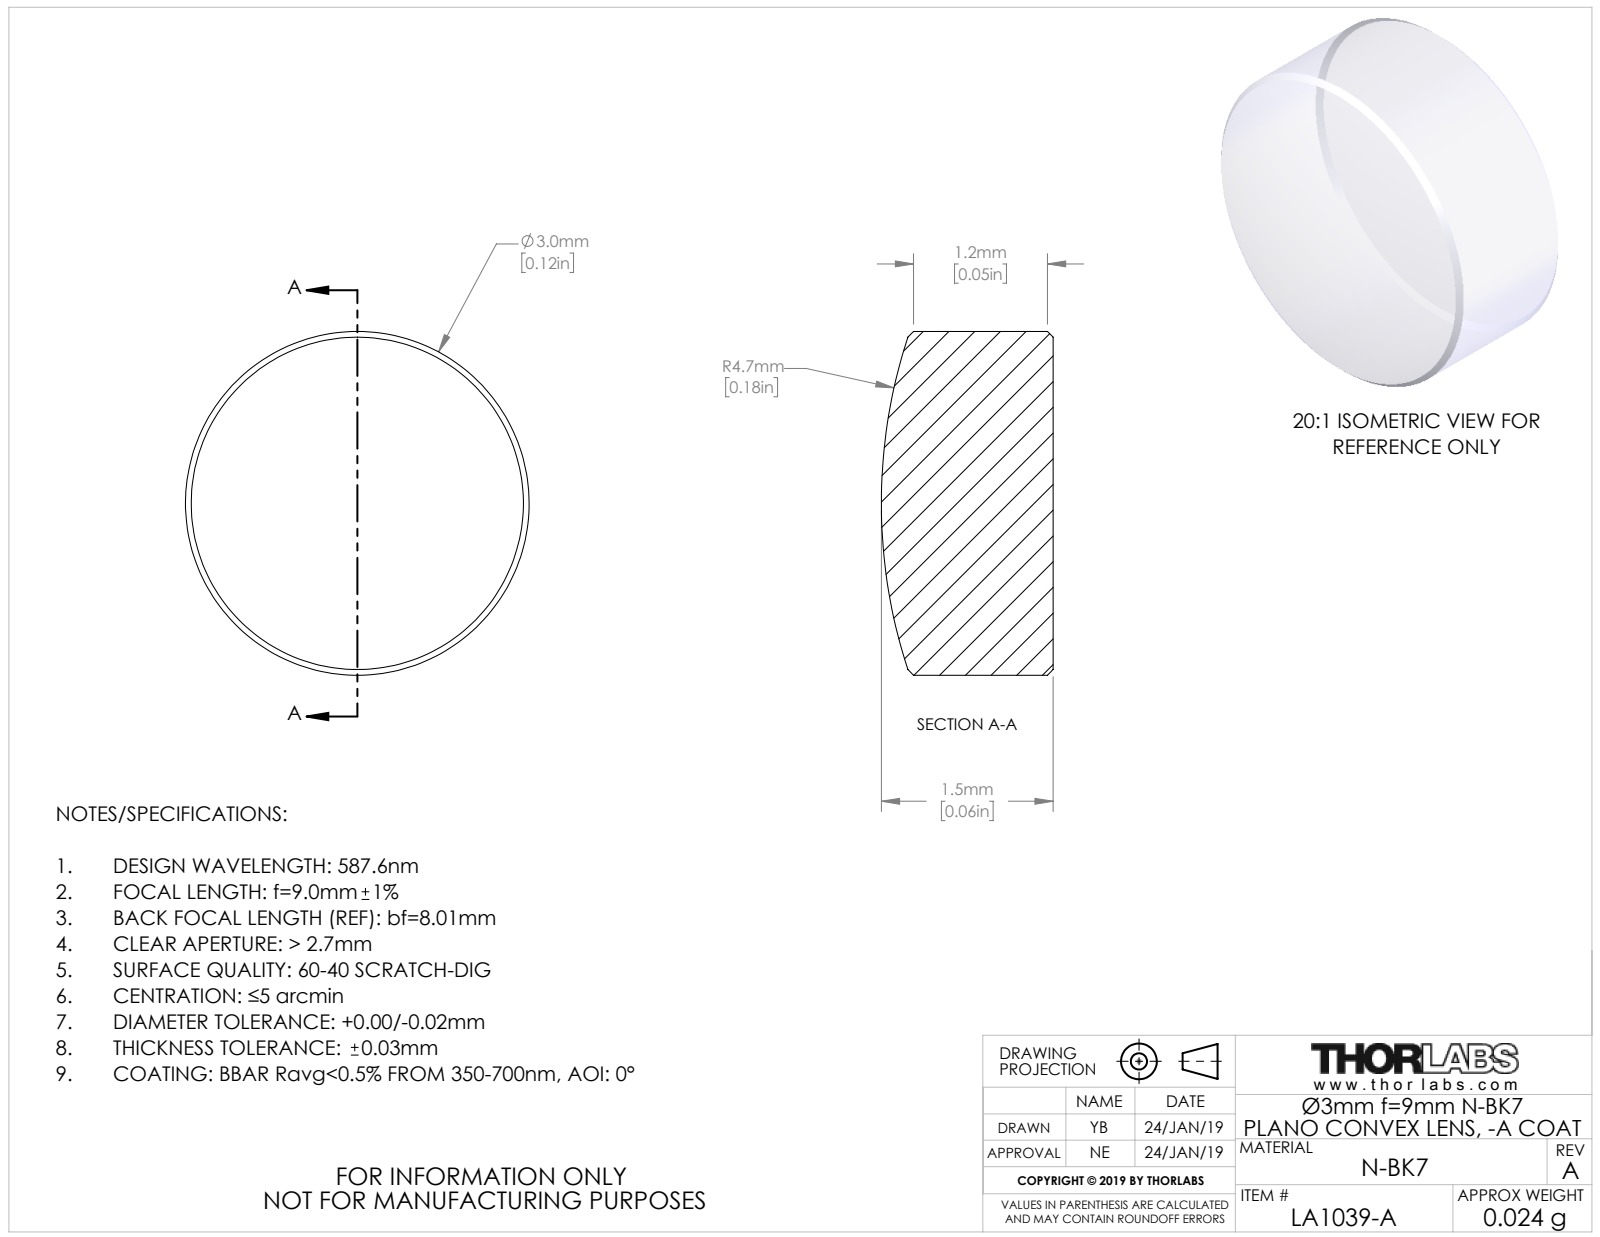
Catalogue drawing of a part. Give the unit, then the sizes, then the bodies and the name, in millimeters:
Units: millimetres
Overall size (bounding box): 3 × 3 × 1.5
Round bosses / shafts (diameter × count): ⌀3 ×1
Volume: 10 mm³ · Surface area: 26 mm²
Bodies: 1 solid, 9 faces (1 planar, 2 cylindrical, 6 other)
Part name (STEP PRODUCT): TTN162587-E0W
STEP written by: SolidWorks 2018 (CONFIG_CONTROL_DESIGN)
